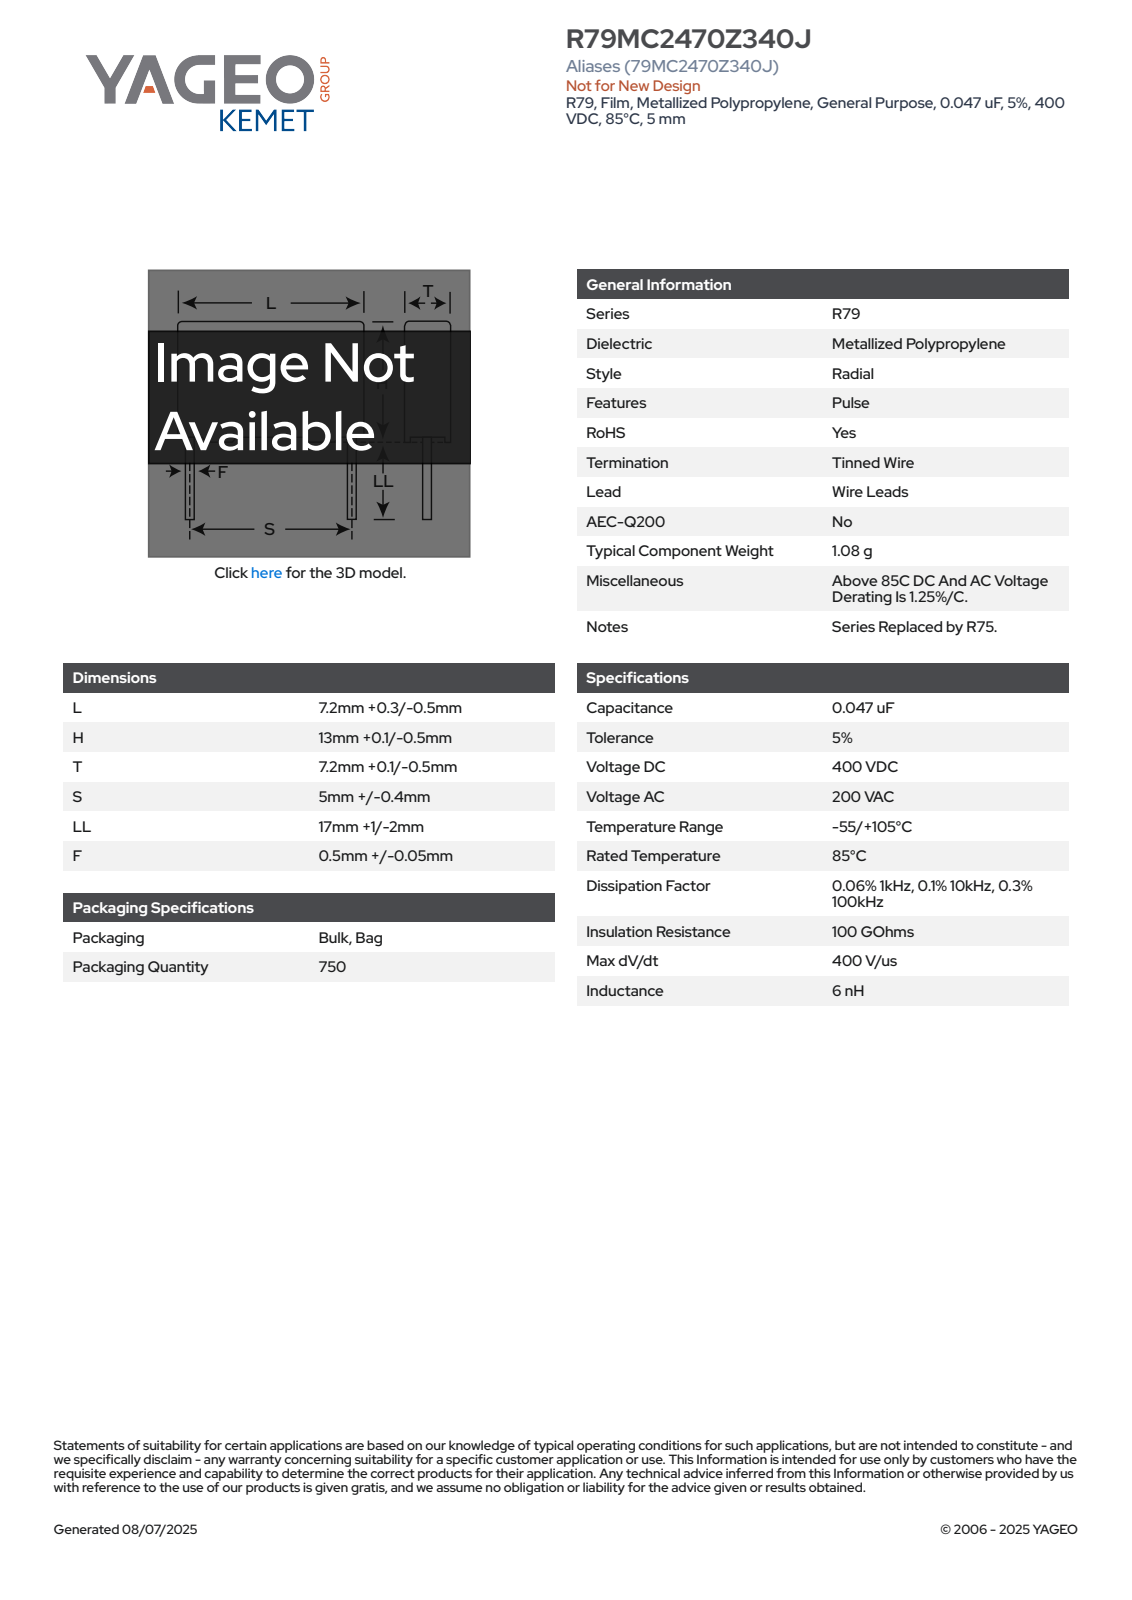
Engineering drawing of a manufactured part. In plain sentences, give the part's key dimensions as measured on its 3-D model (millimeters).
The part is named "CFR_RB2_7.2X13X7.2_L7.5H13.1T7.3S5LL18F0.55". Its 3-D file was written by "SolidWorks 2021 (AUTOMOTIVE_DESIGN)". It is 4 solids with 85 faces: 77 planar, 8 cylindrical and 0 other. Overall it measures 31.1 by 7.5 by 7.3 millimeters. Its volume is 688 cubic millimeters and its surface area 578 square millimeters. Round bosses or shafts: 2 of diameter 0.55. Partial cylindrical surfaces (rounded edges, fillets, slot ends): 4 of radius 0.5. The main face-to-face distances are 7.3, 7.5, 12.35, 7.25, 7.05, 0.75, 13.1, 7, 6.8, 0.45.
